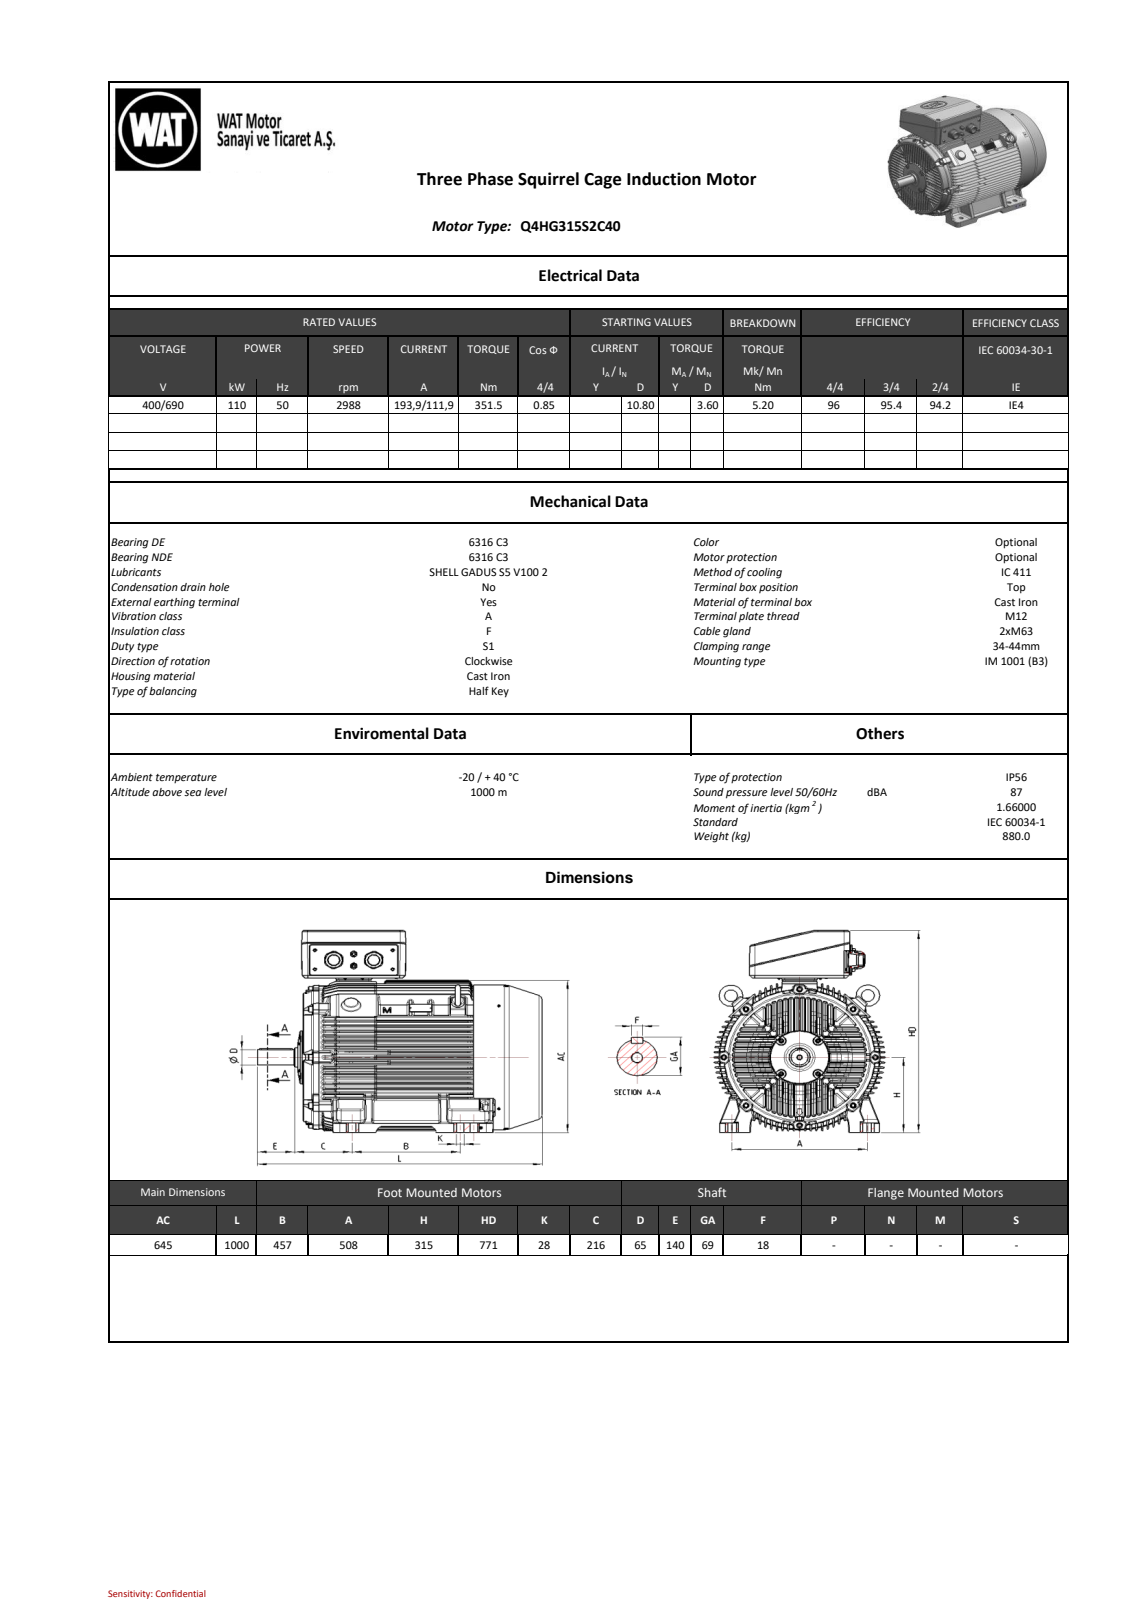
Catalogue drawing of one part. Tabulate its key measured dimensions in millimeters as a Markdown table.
| quantity | value |
| --- | --- |
| part name | 26009910674F4pfn |
| STEP written by | SIEMENS PLM Software NX 11.0 (AUTOMOTIVE_DESIGN) |
| units | millimeters |
| bodies | 0 solids, 8937 faces (3653 planar, 1853 cylindrical, 3431 other) |
| overall size | 1000 × 847.37 × 645 |
| round holes (diameter × count) | 20 × 6, 8.5 × 4, 8 × 3, 4 × 2, 8.8 × 2, 9 × 2, 12 × 2, 18 × 2, 44 × 2, 44.4 × 2, 44.5 × 2, 47.7 × 2 |
| round bosses / shafts (diameter × count) | 24 × 8, 16 × 8, 10 × 8, 20 × 4, 64.8 × 2, 50 × 2, 607 × 1, 565 × 1 |
| partial cylindrical surfaces (radius × count) | 6 × 743, 3 × 199, 1.5 × 148, 2.09 × 59, 2.61 × 54, 0.8 × 36, 15 × 34, 10 × 28 |
| main face-to-face distances | 117, 20.8, 263.64, 1.5, 115.5, 41.69, 20.89, 242.75, 221.95, 20.71 |
| hole center spacings | 79.06, 150, 79.05, 669, 0.33, 21, 30, 50 |
